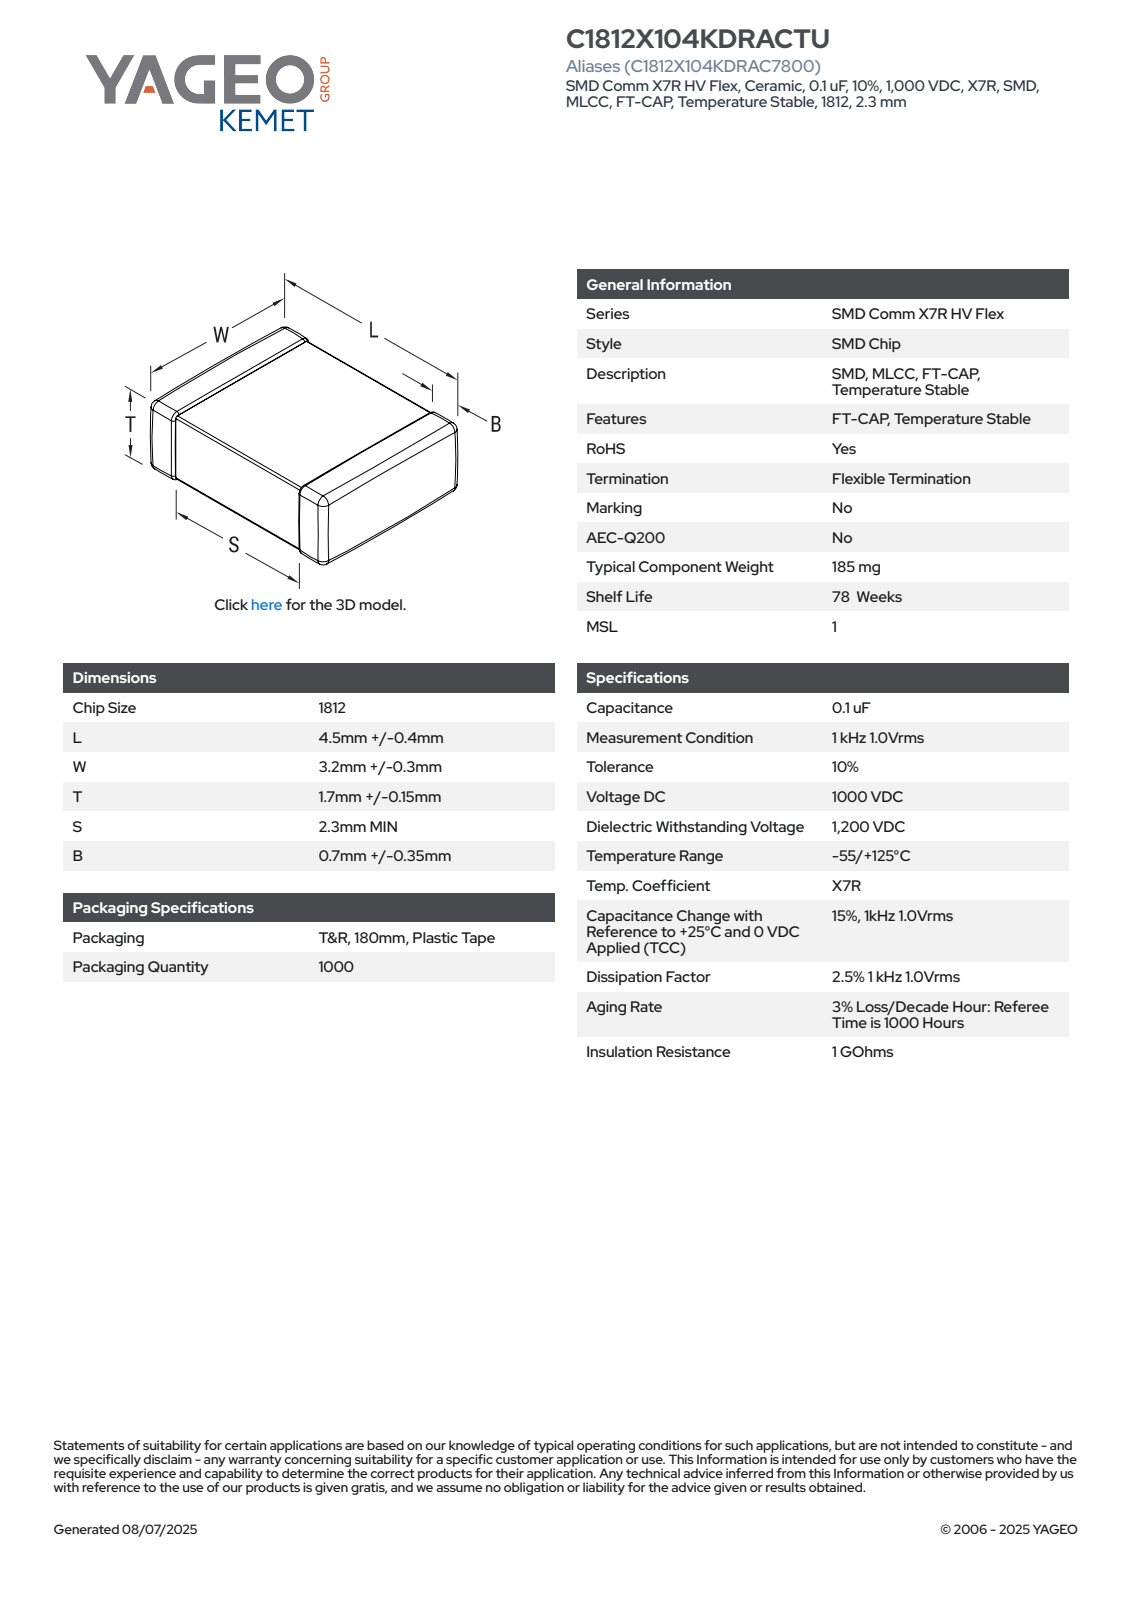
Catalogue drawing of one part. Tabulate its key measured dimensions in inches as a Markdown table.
| quantity | value |
| --- | --- |
| part name | CCS_CCSTDNOS_1812_L4.9W3.5T1.85B1.05 |
| STEP written by | SolidWorks 2014 (AUTOMOTIVE_DESIGN) |
| units | inches |
| bodies | 4 solids, 125 faces (71 planar, 38 cylindrical, 16 other) |
| overall size | 0.193 × 0.138 × 0.073 |
| volume | 0.002 in³ |
| surface area | 0.099 in² |
| main face-to-face distances | 0.07, 0.067, 0.135, 0.073, 0.193, 0.132, 0.138, 0.056, 0.076, 0.059 |
